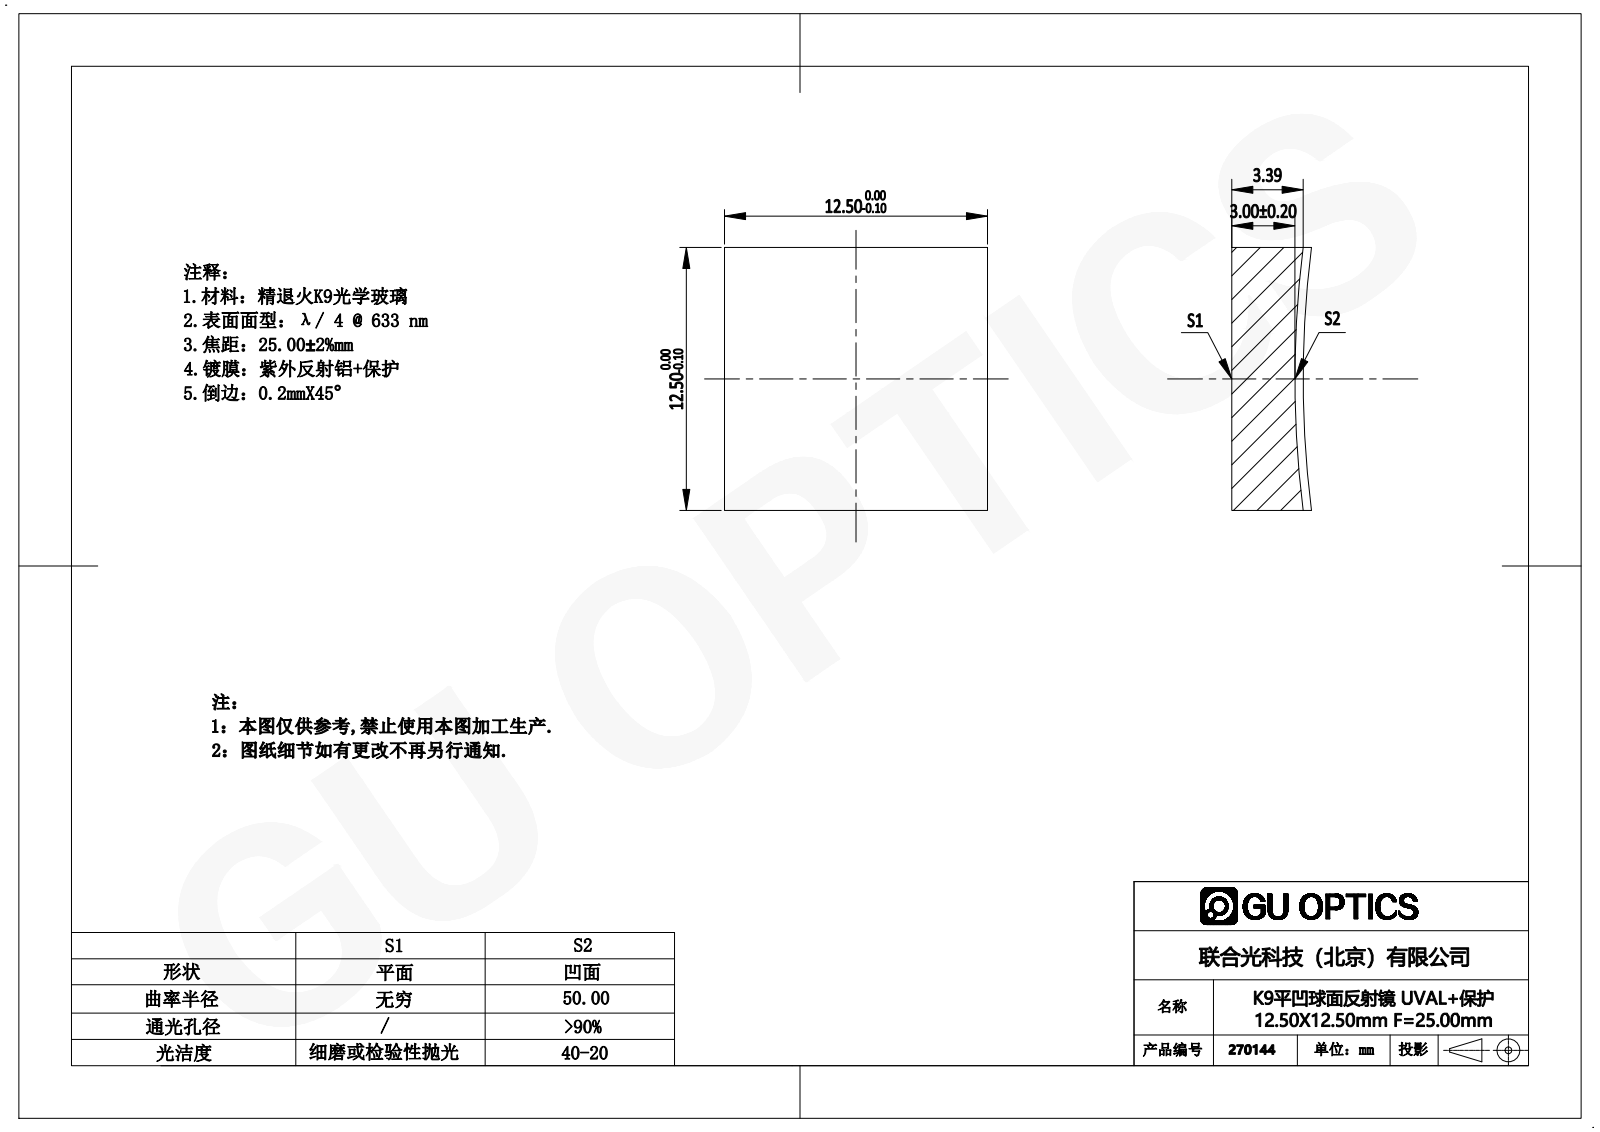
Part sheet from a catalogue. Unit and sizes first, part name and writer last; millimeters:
Units: millimetres
Overall size (bounding box): 12.5 × 12.5 × 3.39
Partial cylindrical surfaces — rounded edges, fillets, slot ends (radius × count): R50 ×1
Main face-to-face distances: 12.5
Volume: 489 mm³ · Surface area: 476 mm²
Bodies: 1 solid, 7 faces (5 planar, 2 cylindrical, 0 other)
Part name (STEP PRODUCT): 270014
STEP written by: SolidWorks 2016 (AUTOMOTIVE_DESIGN)
